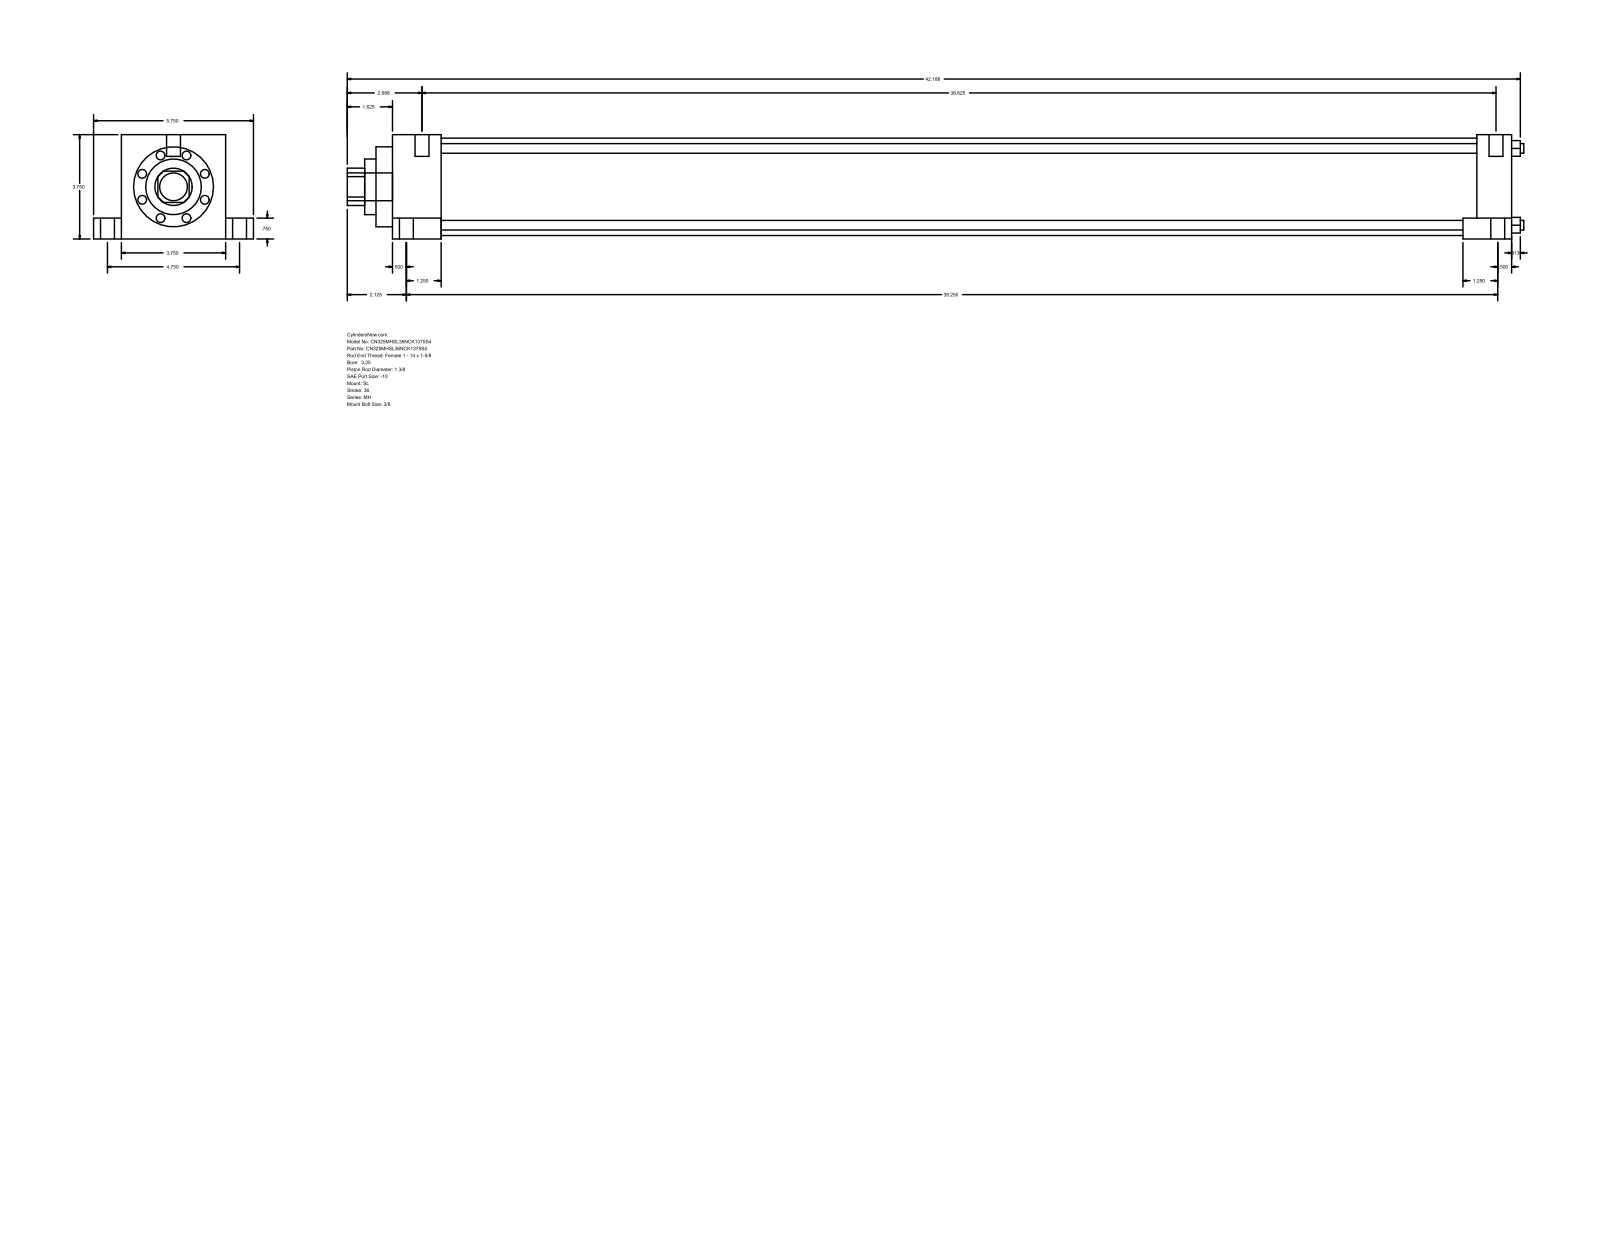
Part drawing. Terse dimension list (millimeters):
name: MH_SL__0325_1.375
written by: GSSL Pune (CONFIG_CONTROL_DESIGN)
unit: mm
bodies: 0 solids, 110 faces (77 planar, 33 cylindrical, 0 other)
size: 1074.74 × 146.05 × 95.25
holes: 4× ⌀8.76, 1× ⌀34.92, 1× ⌀50.8, 1× ⌀73.03, 1× ⌀88.9
bosses: 6× ⌀12.7, 4× ⌀19.05, 4× ⌀5.56, 1× ⌀25.4
rounds: 1× R17.06
face distances: 95.24, 1022.35, 44.45, 977.9, 25.41, 120.65, 19.05, 76.19, 990.61, 946.16
hole spacings: 49.57, 70.1, 99.14
